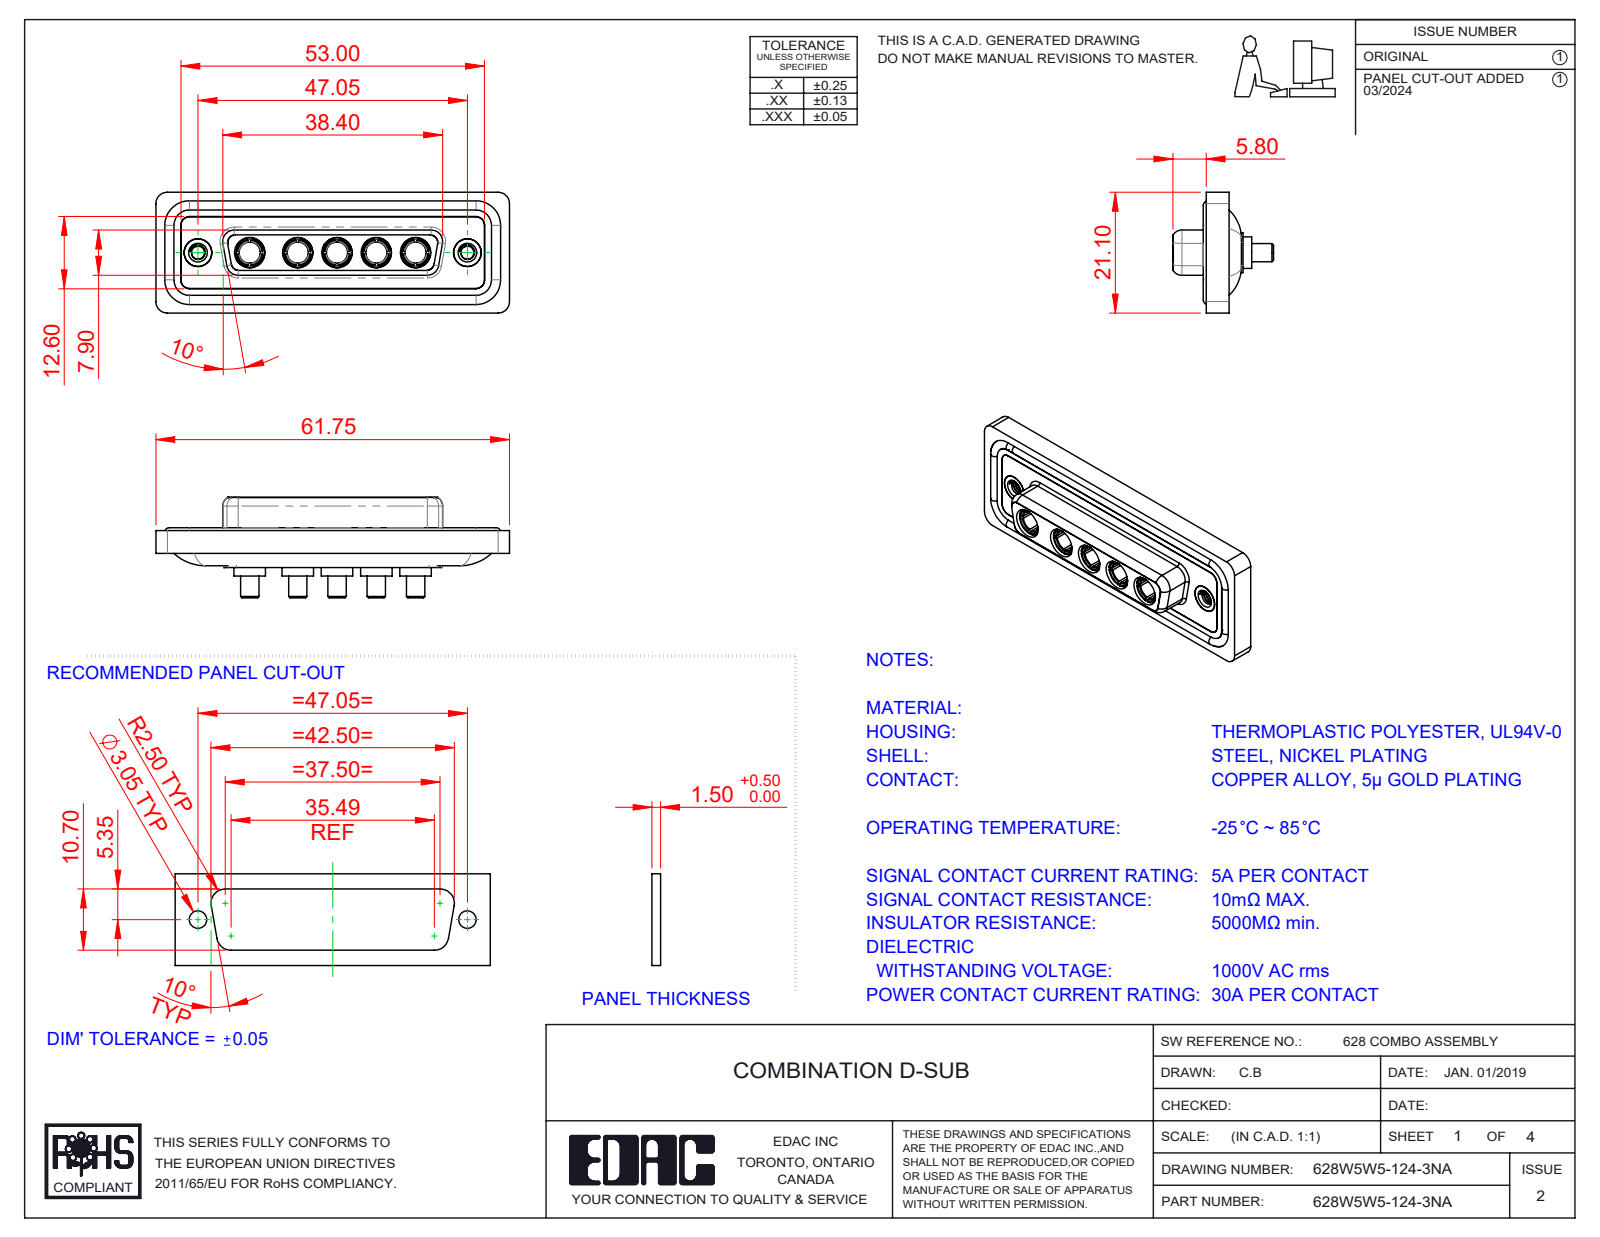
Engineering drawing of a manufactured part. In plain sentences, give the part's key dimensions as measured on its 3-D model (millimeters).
The part is named "628W5W5-124-3NA; 628Combo Threaded Rivet_A; 628Combo Housing_5W5; 628Combo Waterproof Housing_25 Contacts (+3 more)". Its 3-D file was written by "SolidWorks 2023 (CONFIG_CONTROL_DESIGN)". It is 17 solids with 754 faces: 250 planar, 305 cylindrical and 199 other. Overall it measures 61.75 by 21.1 by 17.55 millimeters. Its volume is 8 210 cubic millimeters and its surface area 13 436 square millimeters. Round holes: 7 of diameter 4.85, 5 of diameter 3.7, 5 of diameter 5.3, 2 of diameter 2.26, 2 of diameter 4, 2 of diameter 4.05, 2 of diameter 5. Round bosses or shafts: 5 of diameter 5.5, 5 of diameter 5.2, 5 of diameter 4.96, 5 of diameter 4.75, 5 of diameter 3.75, 5 of diameter 3.2, 4 of diameter 1.6, 2 of diameter 4.95. Partial cylindrical surfaces (rounded edges, fillets, slot ends): 22 of radius 1.5, 18 of radius 2, 8 of radius 1.35, 8 of radius 1.6, 5 of radius 2.1, 4 of radius 0.25, 4 of radius 0.5, 4 of radius 0.6. The main face-to-face distances are 0.4, 1.8, 7.45, 5.65, 0.5, 7.05, 6.6, 1.6, 1.1, 2.9. The hole center spacings are 6.86, 9.04, 13.72, 38.01, 8.39, 15.25, 15.9, 17.43.
